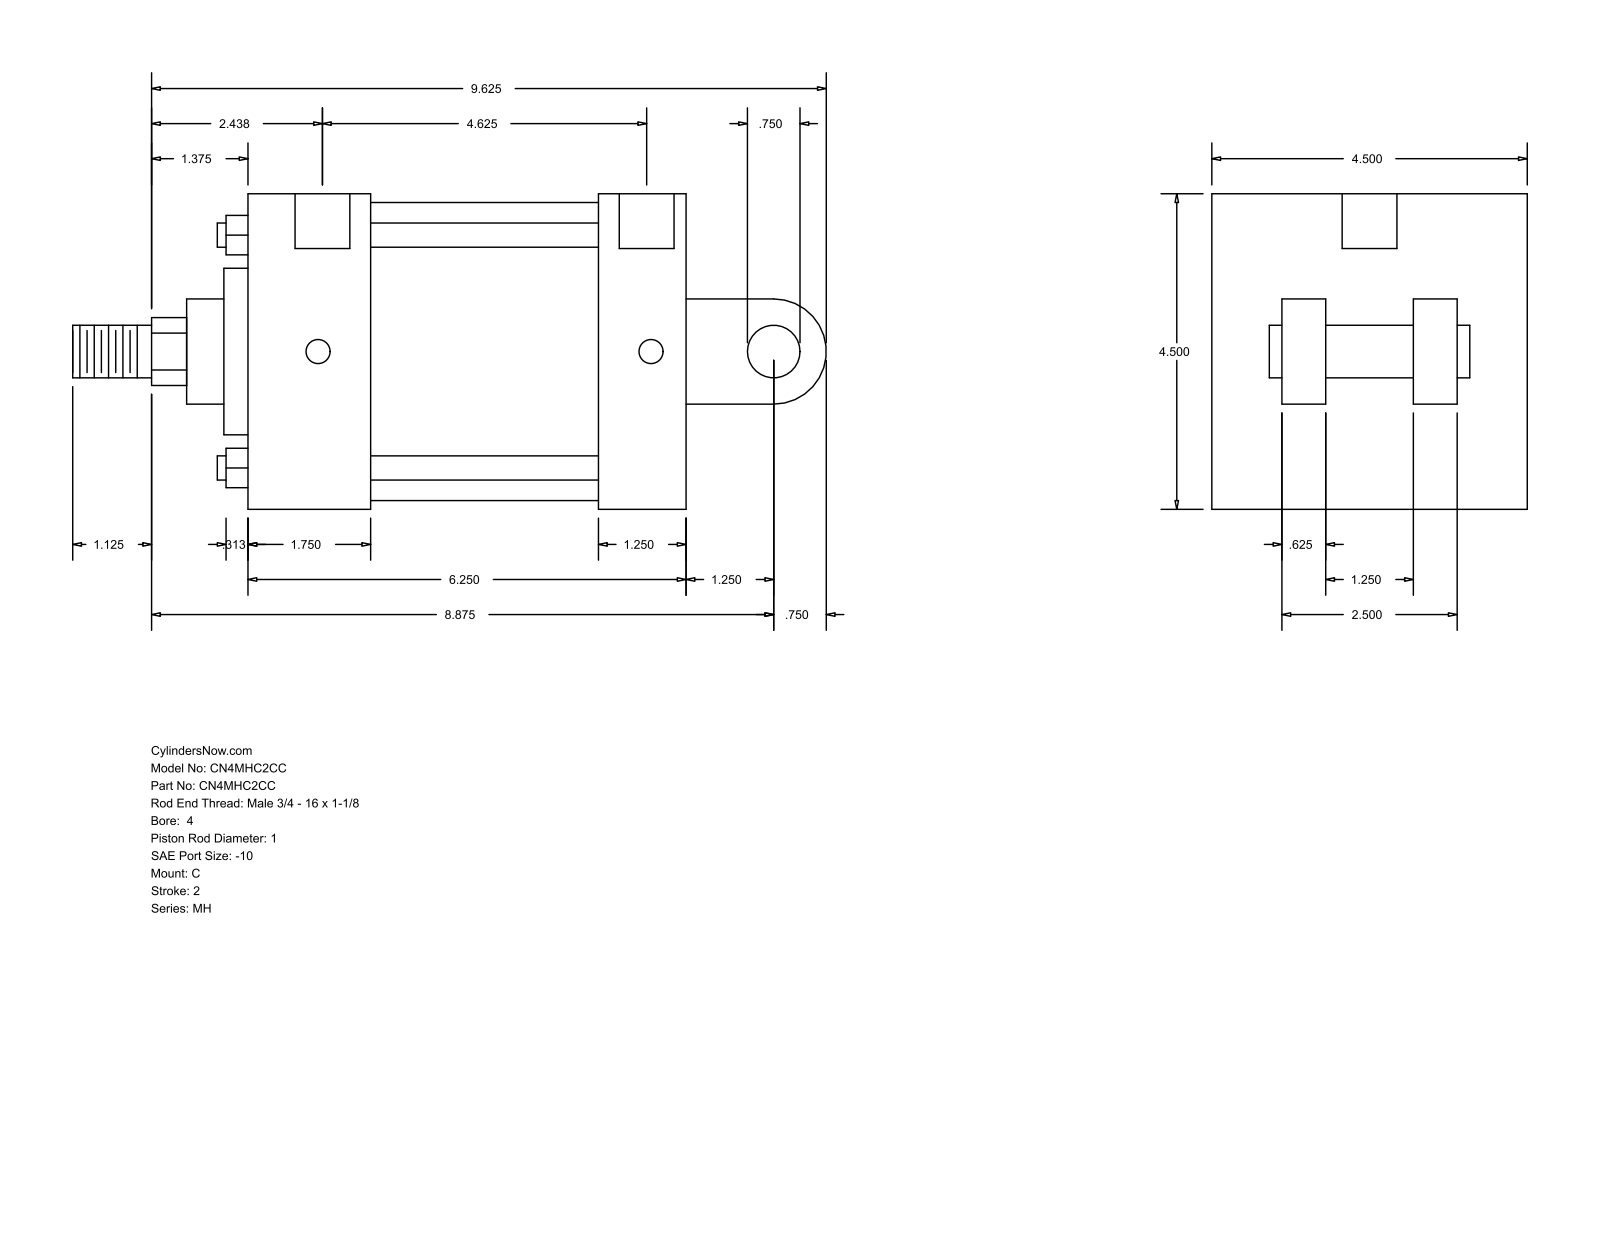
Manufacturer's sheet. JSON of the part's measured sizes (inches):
{"part_name": "MH_C__0400_1", "step_written_by": "GSSL Pune (CONFIG_CONTROL_DESIGN)", "units": "inches", "bodies": {"solids": 0, "faces": 101, "planar": 71, "cylindrical": 30, "other": 0}, "overall_size": [10.75, 4.5, 4.5], "round_holes": [[0.344, 4], [0.781, 2]], "round_bosses_or_shafts": [[0.345, 4], [0.75, 2], [4.25, 1], [2.375, 1], [1.5, 1], [1, 1]], "partial_cylinders_radius": [[0.484, 1], [0.75, 1]], "face_to_face_distances": [4.5, 6.25, 1.75, 5, 3.25, 1.25, 2.875, 1.625, 1.5, 1.875], "hole_center_spacings": [0.062, 4.687, 4.75, 4.625]}
